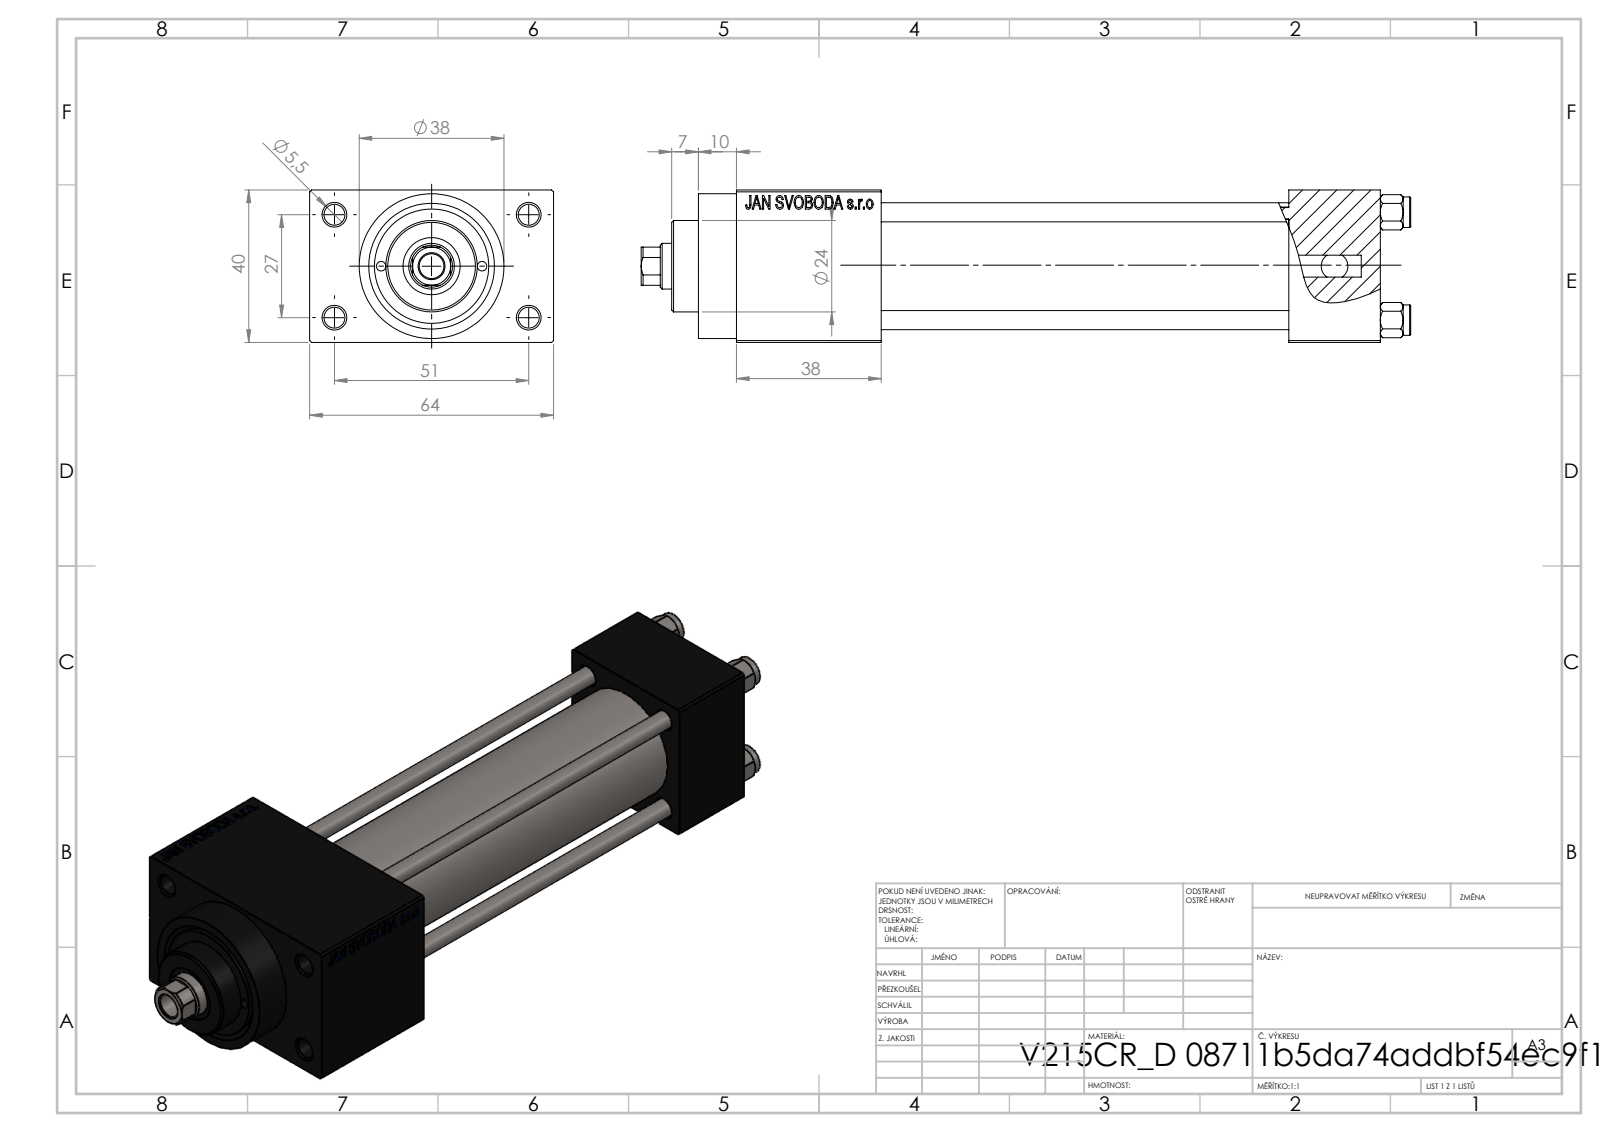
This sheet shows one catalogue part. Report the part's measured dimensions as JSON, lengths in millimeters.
{"part_name": "V215CR_VCP_D; NUT_M5_D; V215CR_D_Body; V215CR_D_TYCINKA (+1 more)", "step_written_by": "SolidWorks 2019 (CONFIG_CONTROL_DESIGN)", "units": "millimeters", "bodies": {"solids": 11, "faces": 1110, "planar": 498, "cylindrical": 92, "other": 520}, "overall_size": [202, 64, 40], "volume_mm3": 200856, "surface_area_mm2": 78746, "round_holes": [[5, 4], [5.5, 4], [20, 3], [2.5, 2], [7, 2], [13.16, 2], [6.5, 1], [12, 1], [15, 1], [25, 1], [30, 1]], "round_bosses_or_shafts": [[8, 4], [38, 1], [31, 1], [24, 1]], "partial_cylinders_radius": [[5.5, 1]], "face_to_face_distances": [40, 12, 107, 24, 131, 52, 38, 169, 145, 64], "hole_center_spacings": [11.37, 14.18, 18.23, 20.01, 28.3, 28.85, 29.89, 30.84]}
